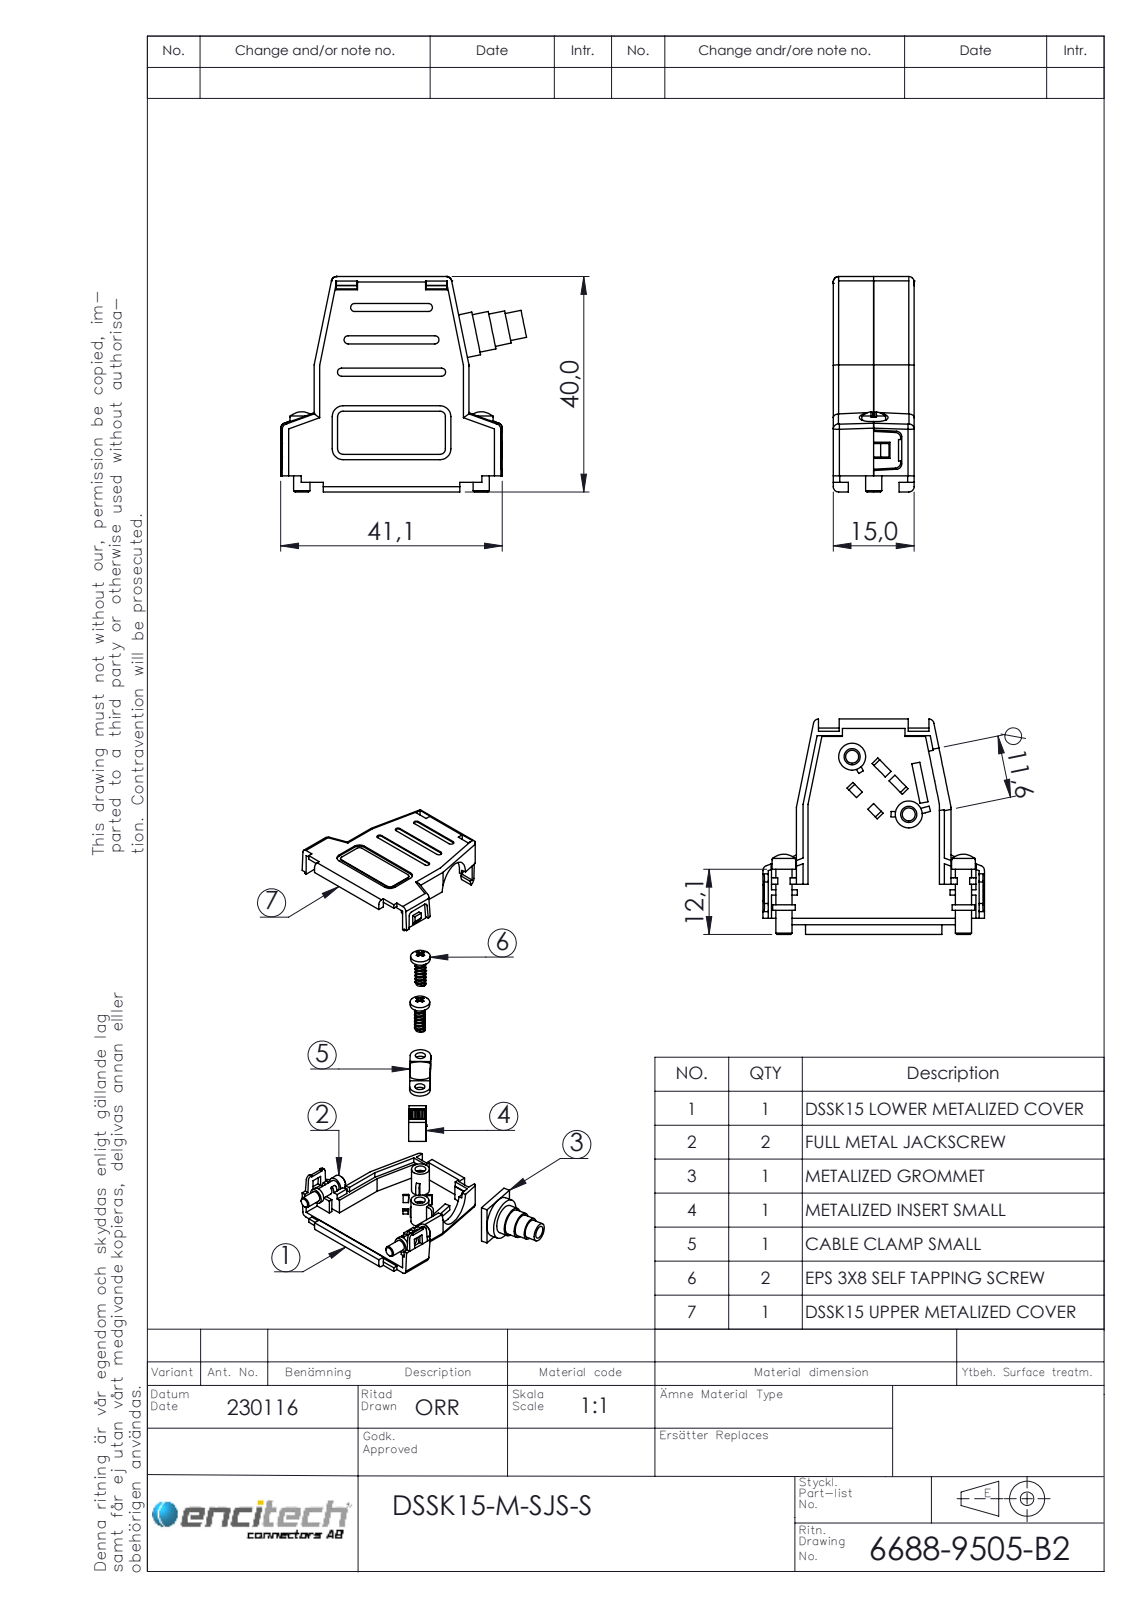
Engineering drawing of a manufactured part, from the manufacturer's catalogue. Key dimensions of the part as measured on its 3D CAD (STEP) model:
Part name (STEP PRODUCT): 6811-0162-05 Part 2; 6811-0162-05 Part 1; 6826-0133-04; 6822-0121-34 (+4 more)
STEP written by: SolidWorks 2021 (AUTOMOTIVE_DESIGN)
Units: millimetres
Bodies: 11 solids, 920 faces (579 planar, 277 cylindrical, 64 other)
Overall size (bounding box): 45.59 × 40 × 15
Volume: 7 498 mm³ · Surface area: 11 479 mm²
Round holes (diameter × count): ⌀2.4 ×2, ⌀2.8 ×2, ⌀3 ×2, ⌀3.5 ×2, ⌀0.75 ×1, ⌀0.9 ×1, ⌀1.25 ×1, ⌀2.5 ×1, ⌀4.5 ×1, ⌀5.5 ×1, ⌀6.5 ×1, ⌀11.6 ×1
Round bosses / shafts (diameter × count): ⌀5.45 ×2, ⌀5 ×2, ⌀4.4 ×2, ⌀4.2 ×2, ⌀3 ×2, ⌀2.46 ×2, ⌀11.3 ×1, ⌀8.1 ×1
Partial cylindrical surfaces — rounded edges, fillets, slot ends (radius × count): R1 ×31, R0.25 ×24, R0.5 ×20, R0.12 ×16, R0.75 ×6, R2 ×6, R0.4 ×4, R1.2 ×4
Main face-to-face distances: 13.3, 1.7, 11.6, 15, 7.5, 5.8, 7.3, 1.5, 1.2, 14.8
Hole centre spacings: 13.58, 7.22, 7.8, 7.86, 8.2, 8.55, 9.26, 9.3
